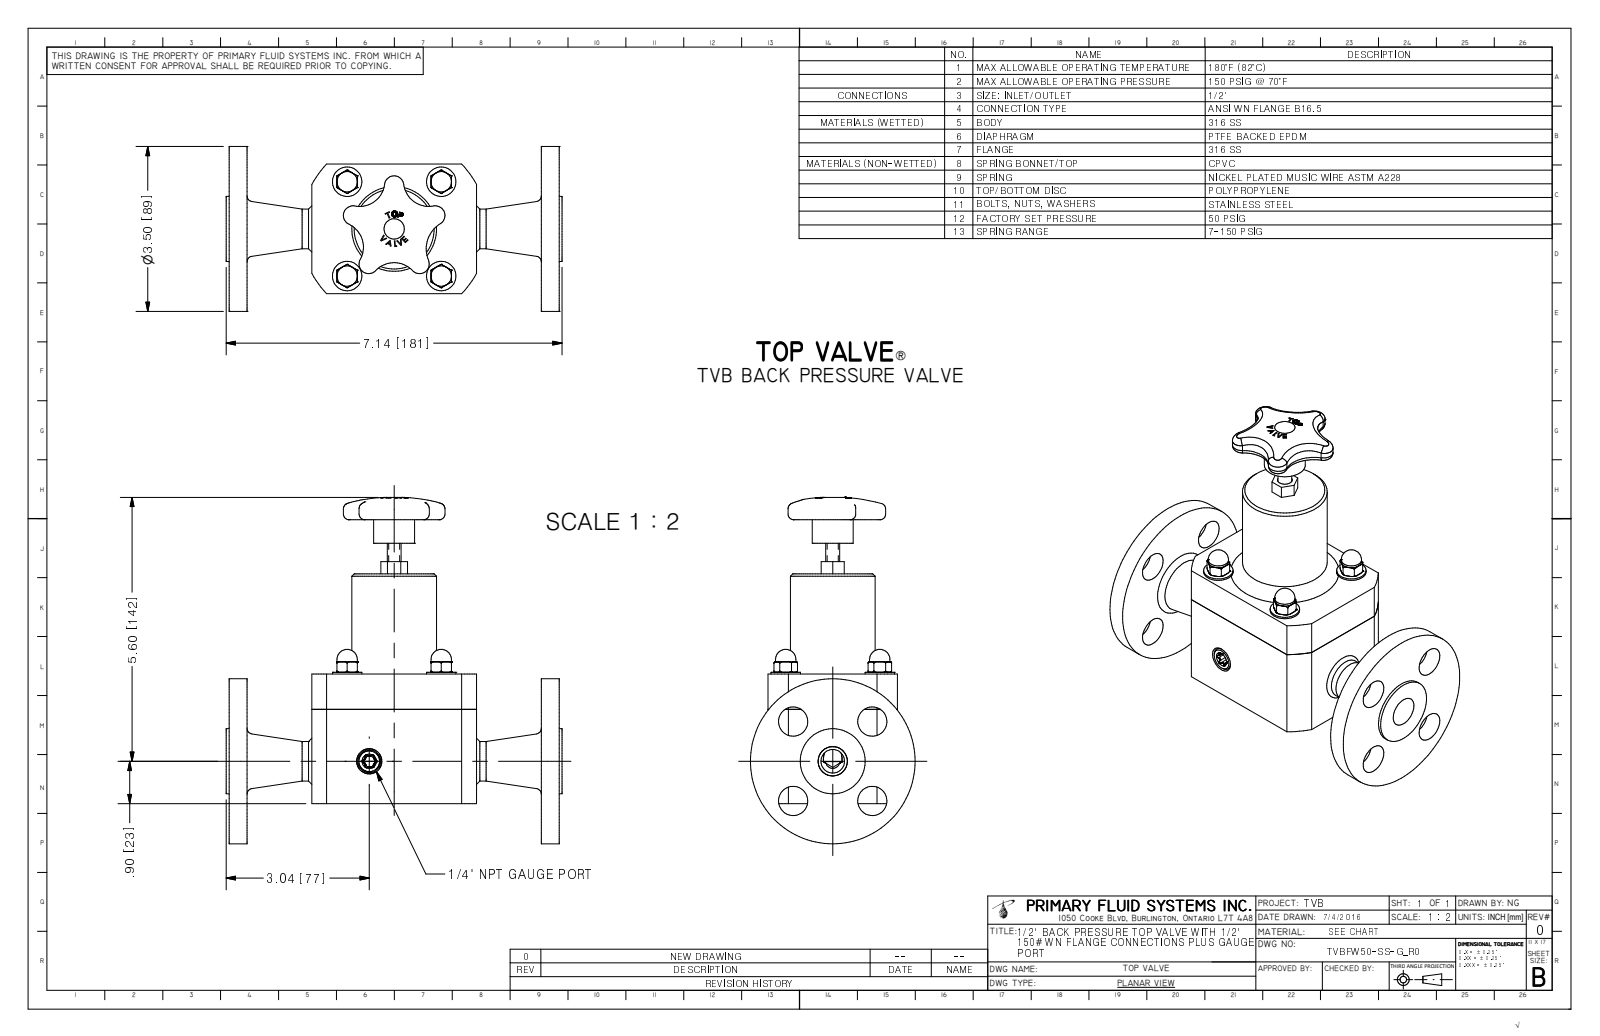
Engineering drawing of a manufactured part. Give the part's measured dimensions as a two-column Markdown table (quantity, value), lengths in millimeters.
| quantity | value |
| --- | --- |
| part name | TVBFW50-SS-G-R0 |
| STEP written by | Autodesk Inventor 2009 (AUTOMOTIVE_DESIGN) |
| units | millimeters |
| bodies | 1 solid, 393 faces (168 planar, 65 cylindrical, 160 other) |
| overall size | 186.6 × 181.4 × 88.9 |
| volume | 661 700 mm³ |
| surface area | 89 610 mm² |
| round holes (diameter × count) | 4.4 × 4, 15.7 × 4, 15.8 × 1 |
| round bosses / shafts (diameter × count) | 15.9 × 4, 11 × 4, 9.5 × 4, 88.9 × 1, 45.7 × 1, 35.1 × 1, 22.1 × 1, 21.3 × 1 |
| partial cylindrical surfaces (radius × count) | 0.7 × 6, 2.2 × 5, 5.2 × 5, 13.6 × 4, 16.7 × 4, 15.9 × 1, 18.9 × 1, 50.5 × 1 |
| main face-to-face distances | 9.7, 168.5, 44.6, 133.5, 35, 123.9, 69.9, 178.2, 158.9, 88.9 |
| hole center spacings | 30.2, 42.7, 50.8, 60.5, 71.8 |
